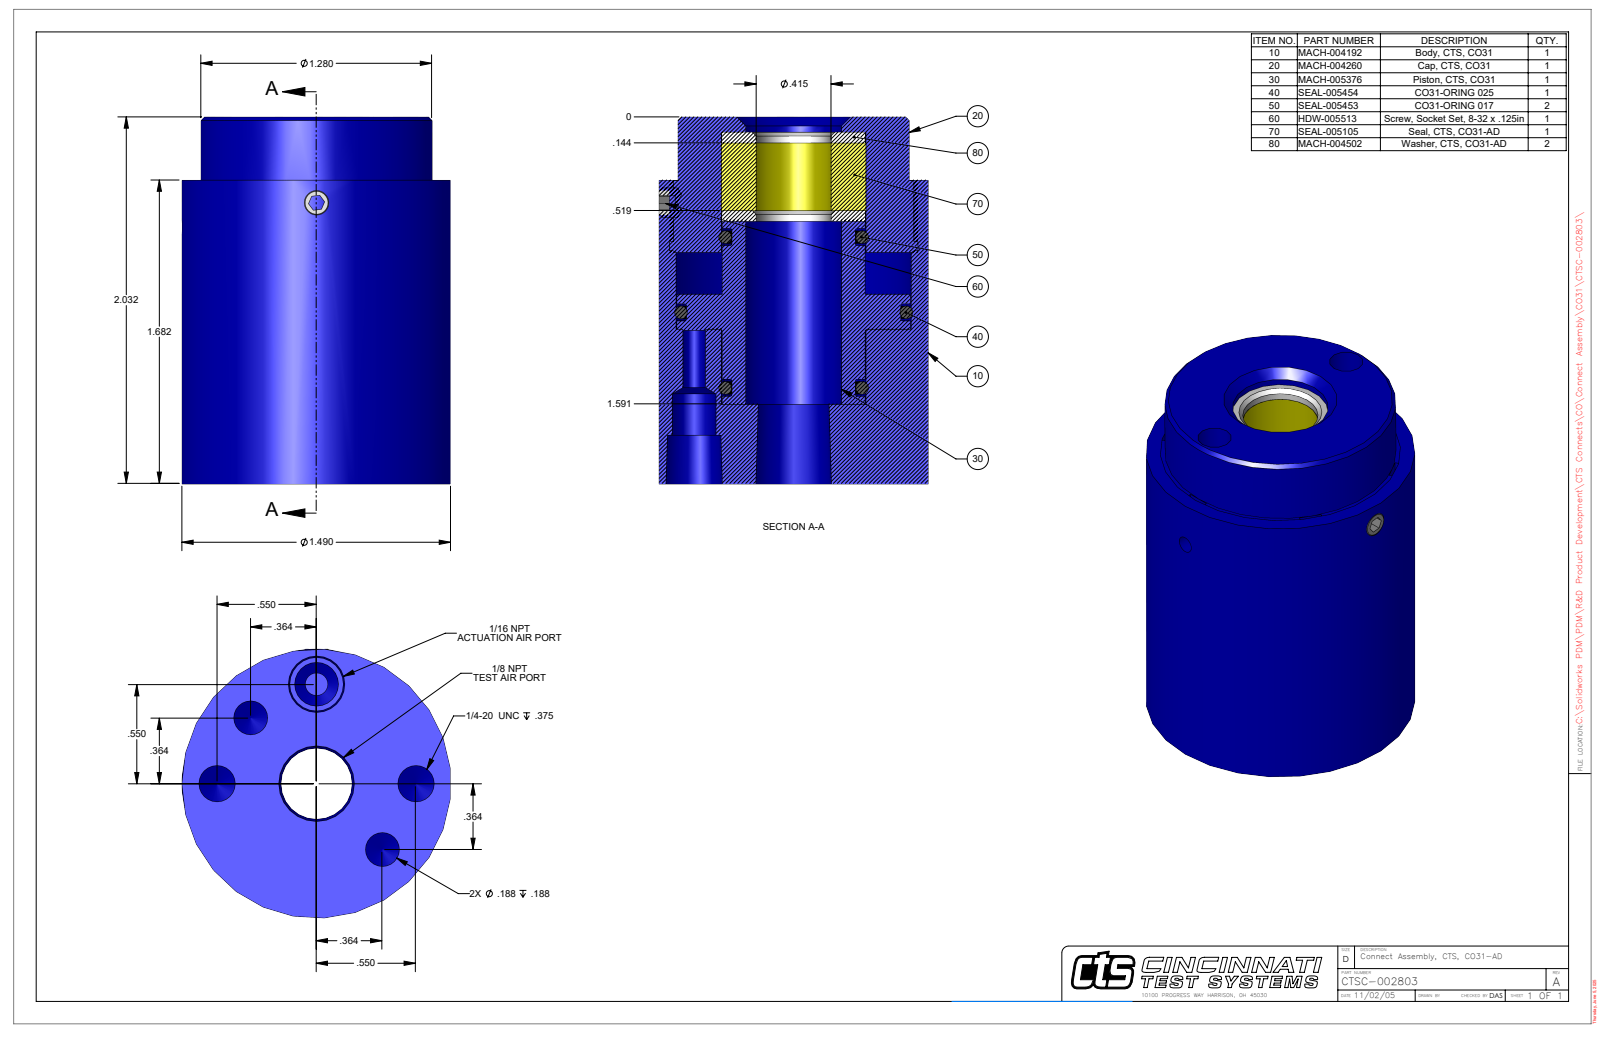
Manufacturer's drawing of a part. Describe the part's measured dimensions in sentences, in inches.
The part is named "CTSC-002803". Its 3-D file was written by "SolidWorks 2023 (AUTOMOTIVE_DESIGN)". It is 1 solid with 111 faces: 53 planar, 40 cylindrical and 18 other. Overall it measures 2.032 by 1.49 by 1.49 inches. Its volume is 2.952 cubic inches and its surface area 17.11 square inches. Round holes: 4 of diameter 0.187, 2 of diameter 0.201, 1 of diameter 0.094, 1 of diameter 0.136, 1 of diameter 0.242, 1 of diameter 0.415, 1 of diameter 0.417, 1 of diameter 0.53, 1 of diameter 0.8, 1 of diameter 1.33. Round bosses or shafts: 1 of diameter 1.49, 1 of diameter 1.28, 1 of diameter 0.792. Partial cylindrical surfaces (rounded edges, fillets, slot ends): 1 of radius 0.687, 1 of radius 0.73. The main face-to-face distances are 2.032, 1.682, 0.35, 0.301, 1.381, 1.731, 0.441, 0.14, 1.241, 1.591. The hole center spacings are 0.515, 0.409, 0.55, 0.984, 0.035, 0.394, 0.754, 0.778.
